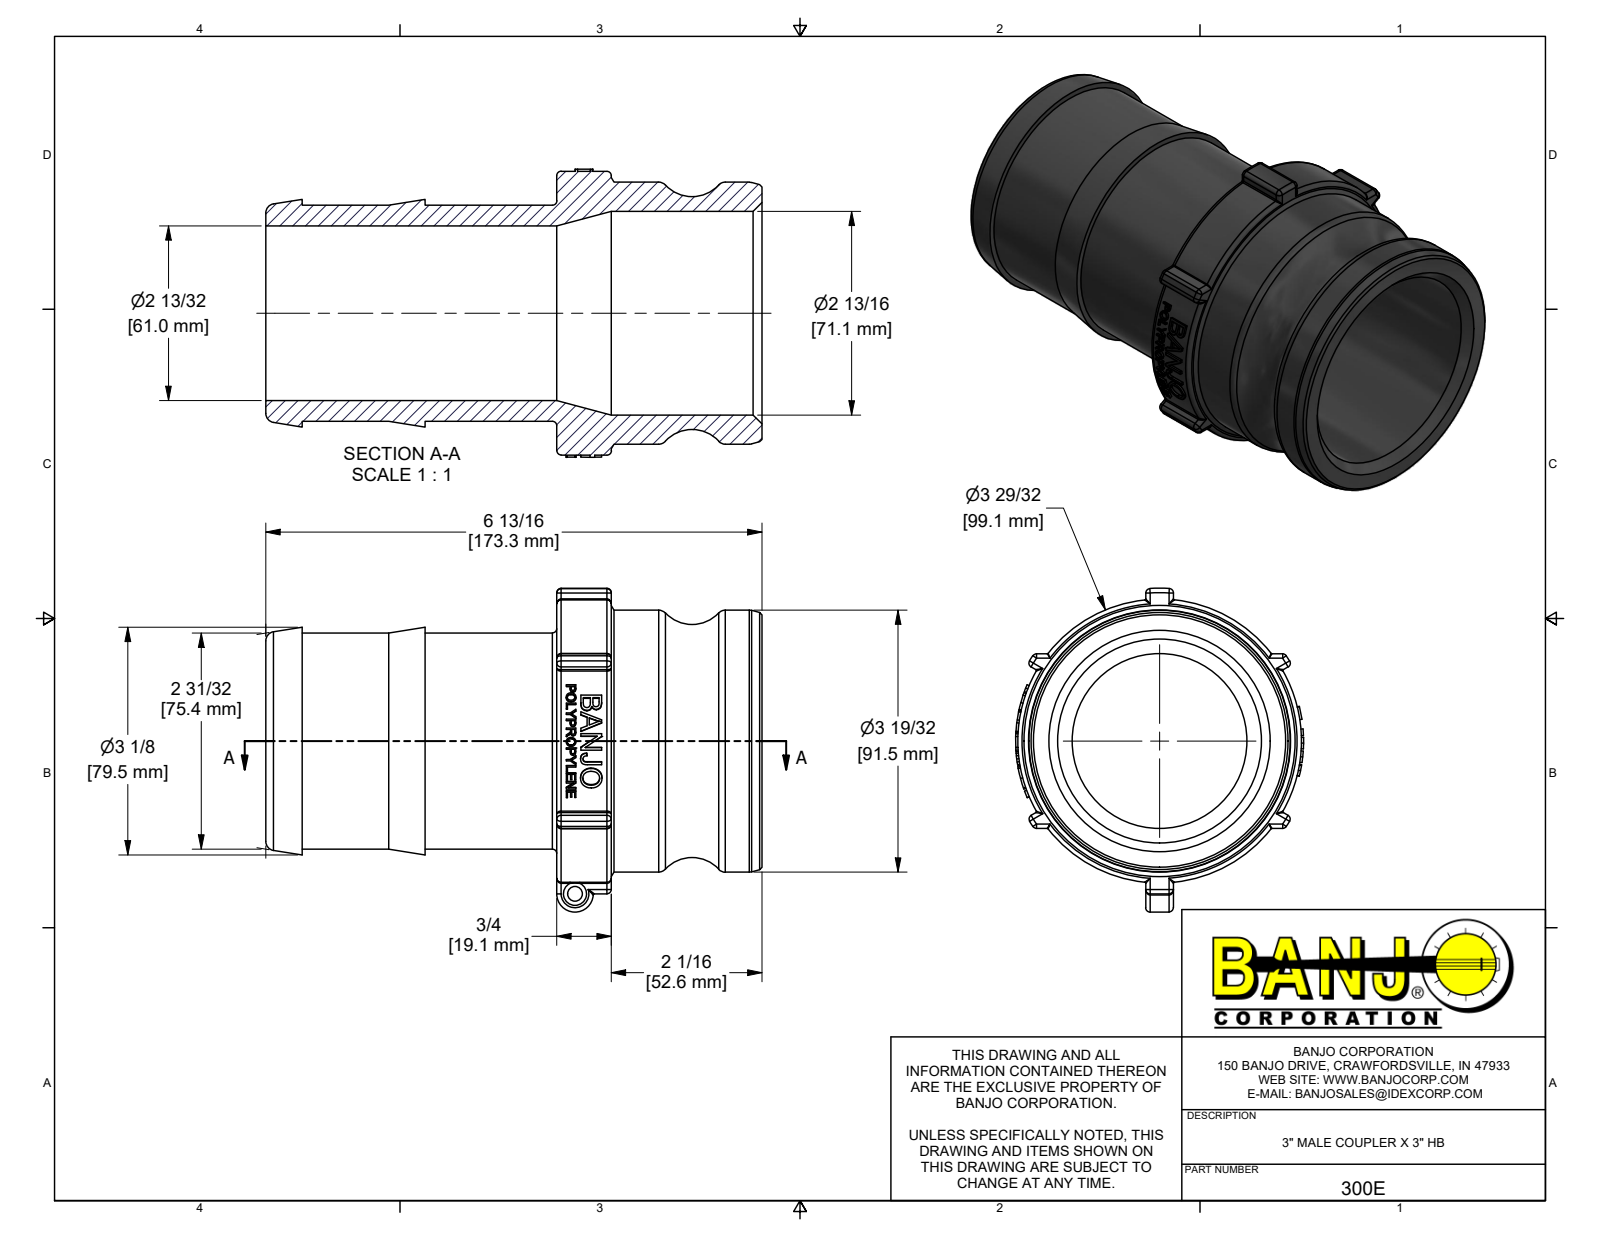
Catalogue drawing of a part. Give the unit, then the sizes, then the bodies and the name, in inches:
Units: inches
Overall size (bounding box): 6.822 × 4.45 × 3.96
Round holes (diameter × count): ⌀0.2 ×1, ⌀2.4 ×1, ⌀2.8 ×1
Round bosses / shafts (diameter × count): ⌀3.9 ×1, ⌀3.602 ×1, ⌀2.97 ×1
Partial cylindrical surfaces — rounded edges, fillets, slot ends (radius × count): R0.06 ×29, R0.016 ×13, R0.25 ×1, R1.98 ×1, R2.1 ×1
Main face-to-face distances: 2.822, 4, 6.822, 0.5, 2.19, 1.69, 3.5, 6.322, 1.81, 4.632
Volume: 22.19 in³ · Surface area: 140.1 in²
Bodies: 1 solid, 458 faces (154 planar, 106 cylindrical, 198 other)
Part name (STEP PRODUCT): 300E; 300EX
STEP written by: Autodesk Inventor 2019 (AUTOMOTIVE_DESIGN)
